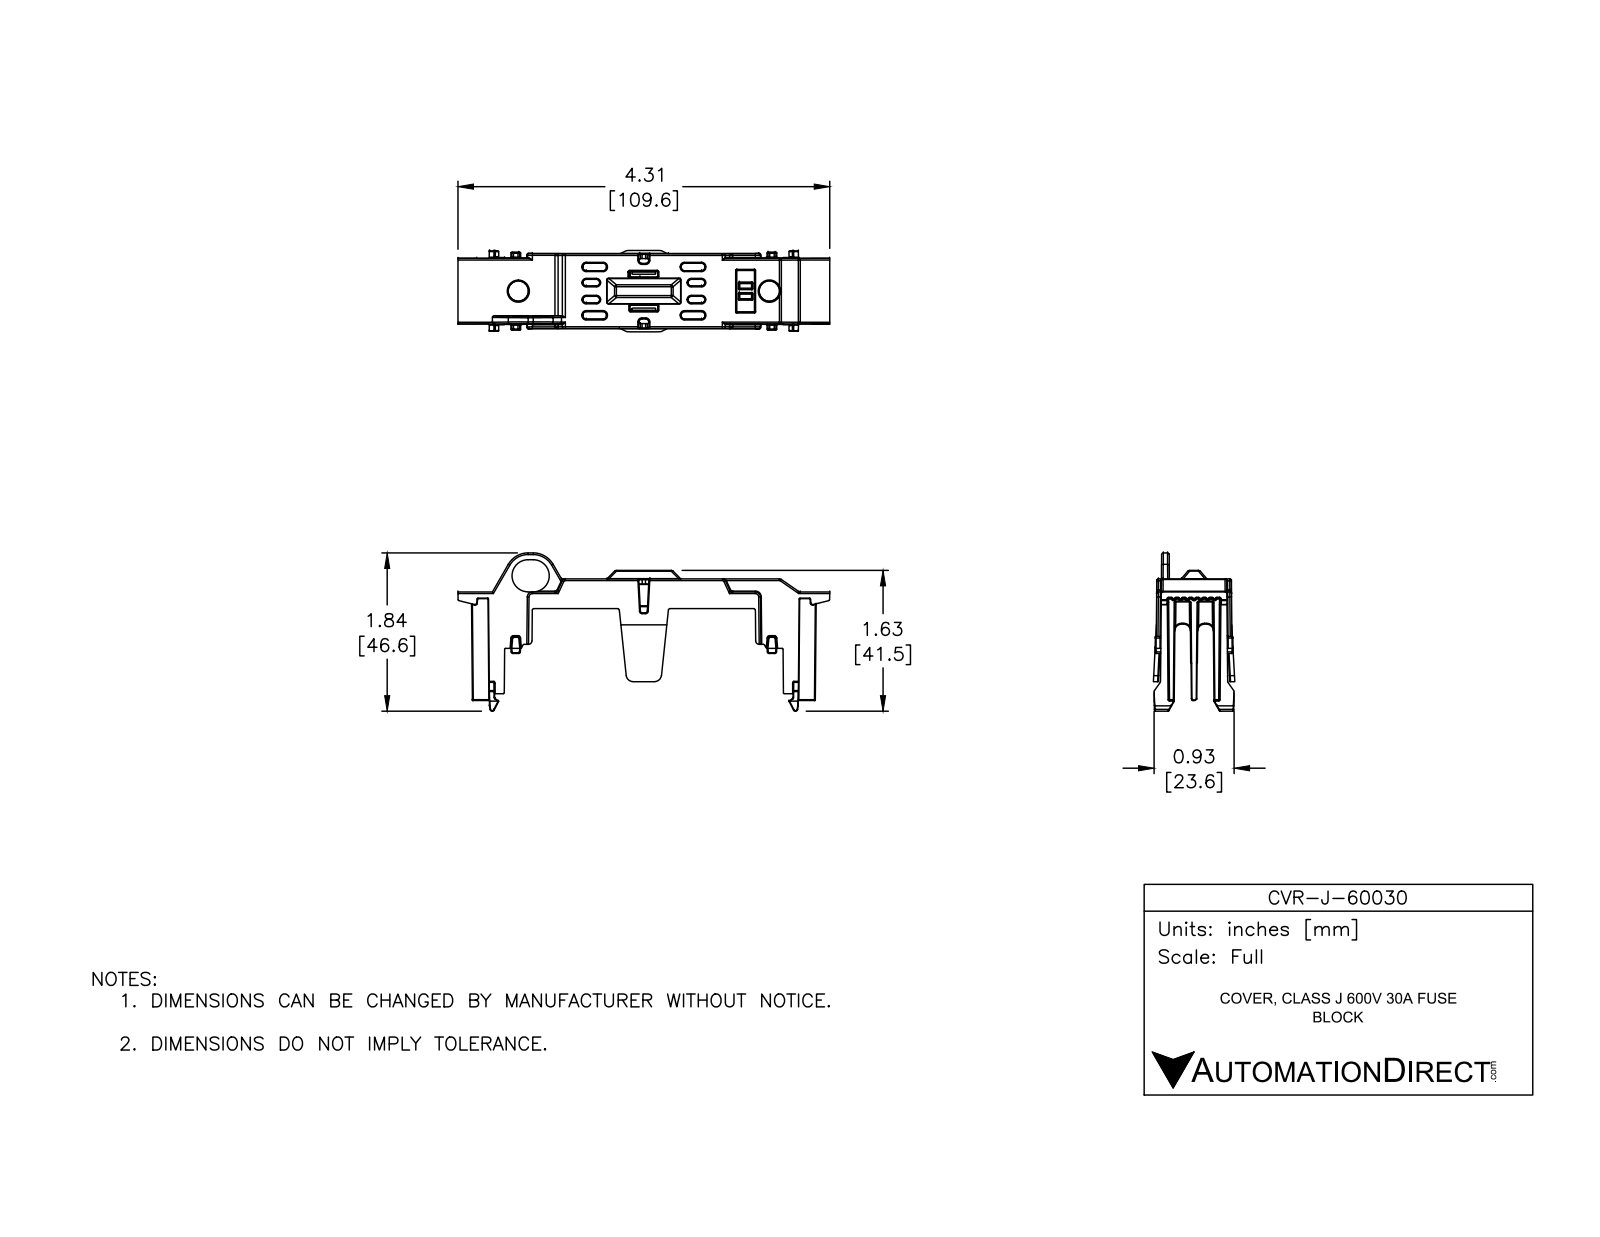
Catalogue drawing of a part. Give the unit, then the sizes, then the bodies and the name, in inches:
Units: inches
Overall size (bounding box): 4.314 × 1.836 × 0.945
Partial cylindrical surfaces — rounded edges, fillets, slot ends (radius × count): R0.01 ×299, R0.006 ×239, R0.02 ×58, R0.039 ×50, R0.03 ×8, R0.079 ×6, R0.004 ×4, R0.026 ×2
Main face-to-face distances: 0.059, 0.054, 0.113, 0.152, 0.059, 0.215, 0.101, 0.155, 0.161, 0.093
Volume: 0.688 in³ · Surface area: 23.6 in²
Bodies: 1 solid, 2037 faces (407 planar, 912 cylindrical, 718 other)
Part name (STEP PRODUCT): CVR-J-60030
STEP written by: SolidWorks 2016 (AUTOMOTIVE_DESIGN)
